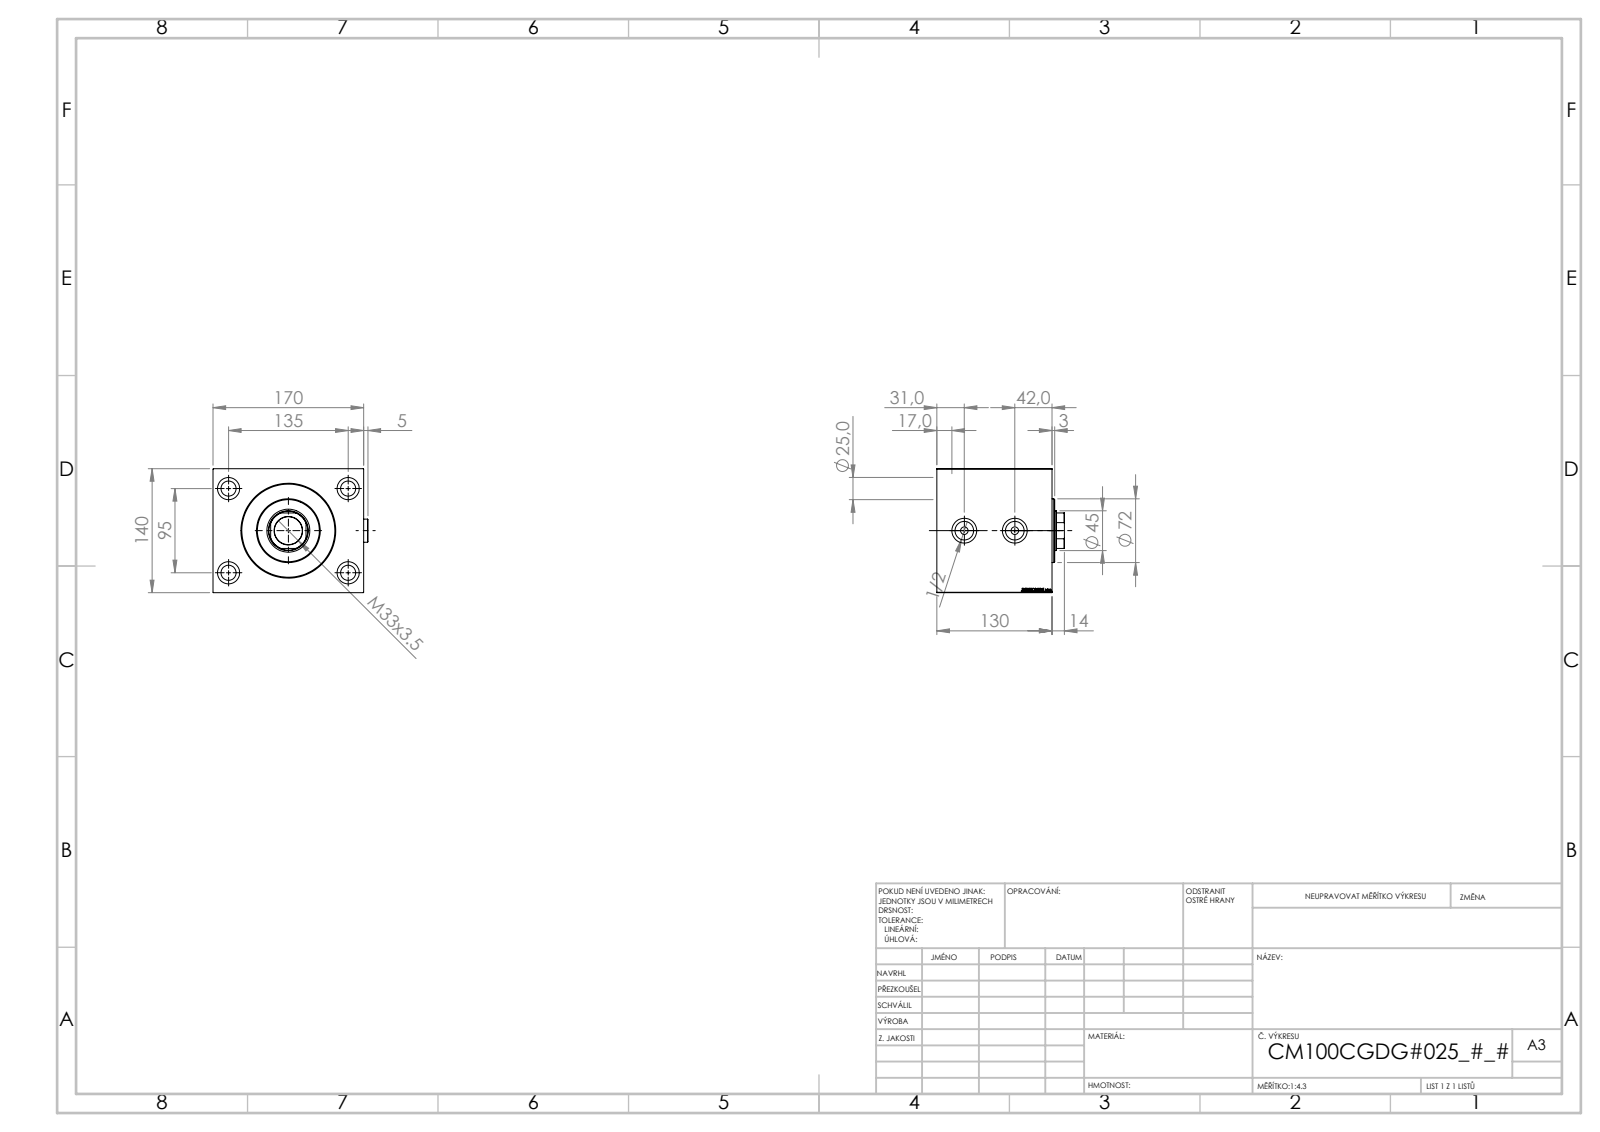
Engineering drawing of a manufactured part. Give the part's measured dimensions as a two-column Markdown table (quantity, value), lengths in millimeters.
| quantity | value |
| --- | --- |
| part name | Zatka_OIL_PORT; V450CM_C_Body; V450CM_C_VCP; V450CM_VC_B |
| STEP written by | SolidWorks 2019 (CONFIG_CONTROL_DESIGN) |
| units | millimeters |
| bodies | 5 solids, 917 faces (443 planar, 76 cylindrical, 398 other) |
| overall size | 174.9 × 144 × 140 |
| volume | 2 849 000 mm³ |
| surface area | 241 943 mm² |
| round holes (diameter × count) | 17 × 4, 25 × 4, 8.5 × 2, 20.96 × 2, 28 × 2, 31.5 × 1, 45 × 1, 48.5 × 1, 100 × 1, 102 × 1, 105 × 1 |
| round bosses / shafts (diameter × count) | 26 × 2, 72 × 1 |
| partial cylindrical surfaces (radius × count) | 22 × 1 |
| main face-to-face distances | 140, 130, 170, 51, 79, 21.6, 29.4, 108.4, 10, 31.6 |
| hole center spacings | 82.54, 95, 135, 165.08, 57 |
